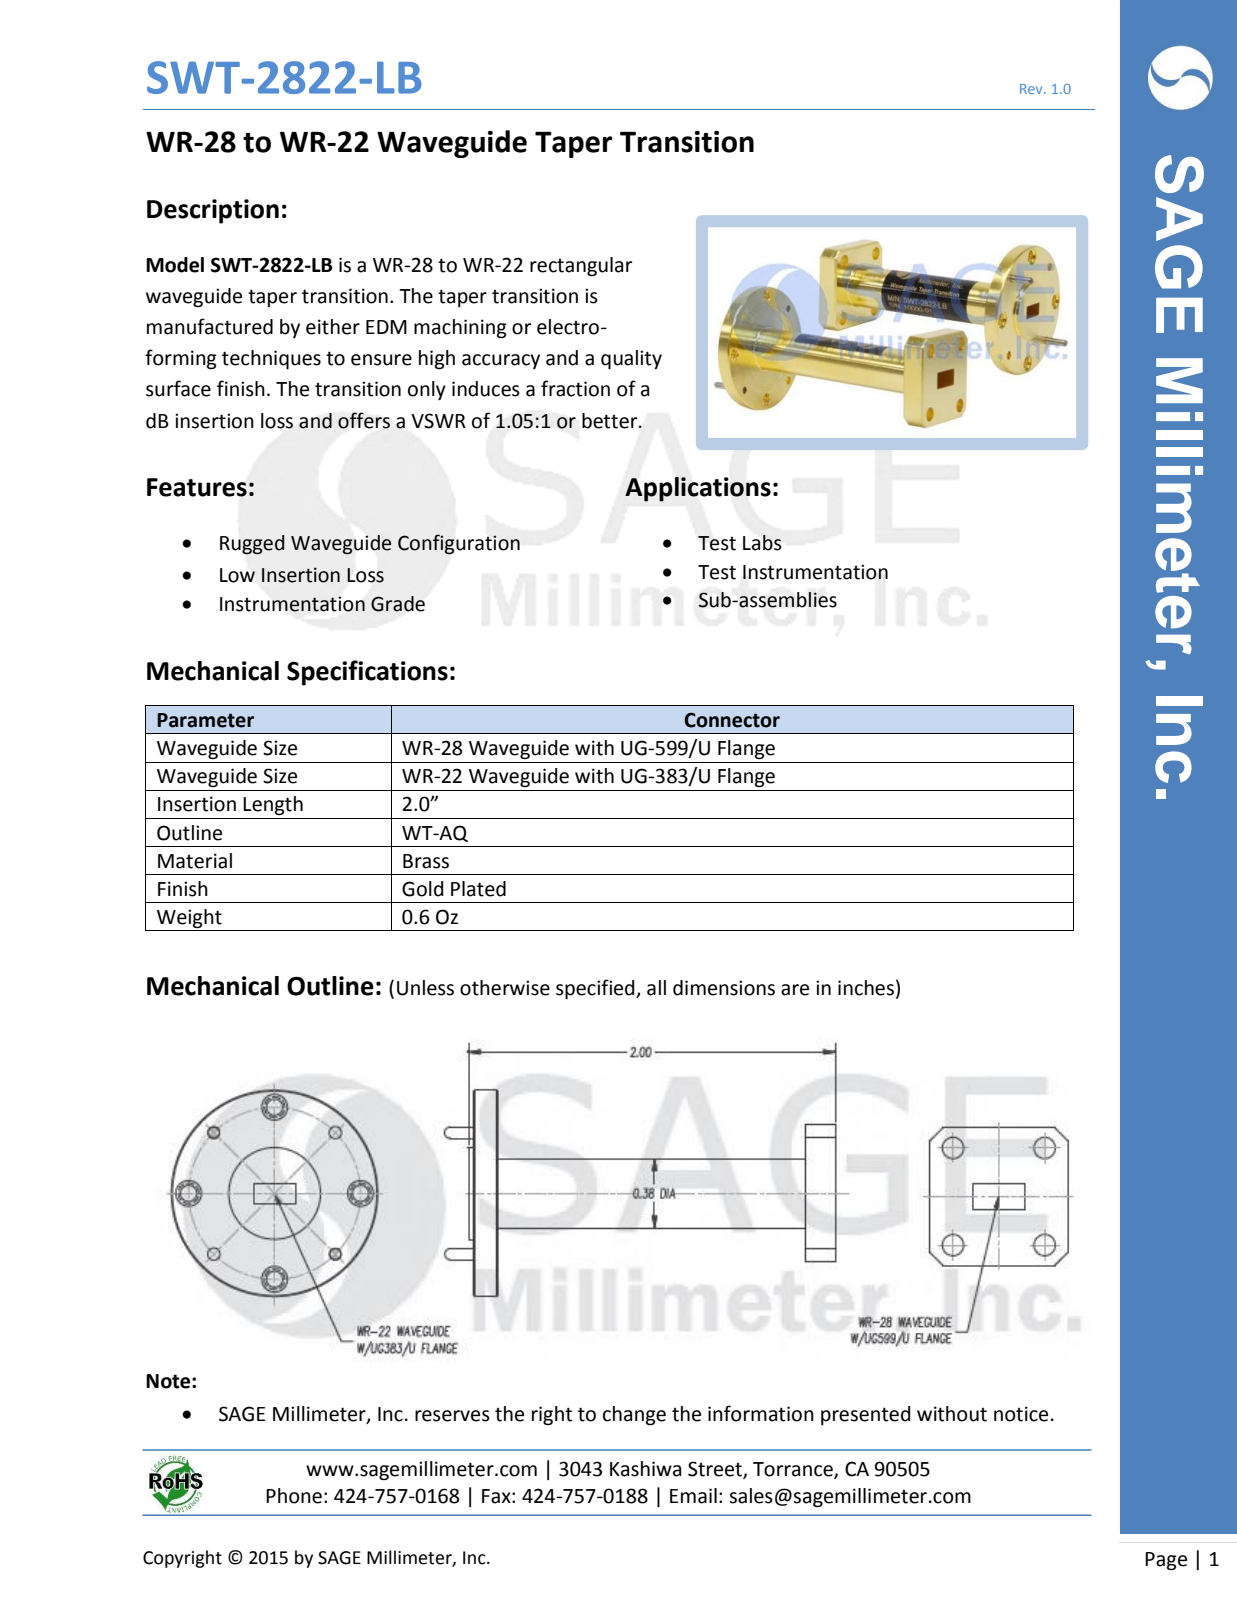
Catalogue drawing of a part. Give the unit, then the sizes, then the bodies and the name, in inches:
Units: inches
Overall size (bounding box): 2.152 × 1.125 × 1.125
Round holes (diameter × count): ⌀0.089 ×4, ⌀0.116 ×4, ⌀0.14 ×4, ⌀0.06 ×2, ⌀0.067 ×2
Round bosses / shafts (diameter × count): ⌀0.063 ×2, ⌀1.125 ×1, ⌀0.5 ×1, ⌀0.38 ×1
Main face-to-face distances: 0.13, 1.84, 1.97, 0.19, 1.65, 1.78, 0.75, 2, 1.81, 0.16
Hole centre spacings: 0.359, 0.866, 0.663, 0.105, 0.322, 0.585, 0.602, 0.766
Volume: 0.351 in³ · Surface area: 7.763 in²
Bodies: 3 solids, 103 faces (41 planar, 42 cylindrical, 20 other)
Part name (STEP PRODUCT): SWT-2822-LB, CTRLD
STEP written by: SolidWorks 2013 (CONFIG_CONTROL_DESIGN)
